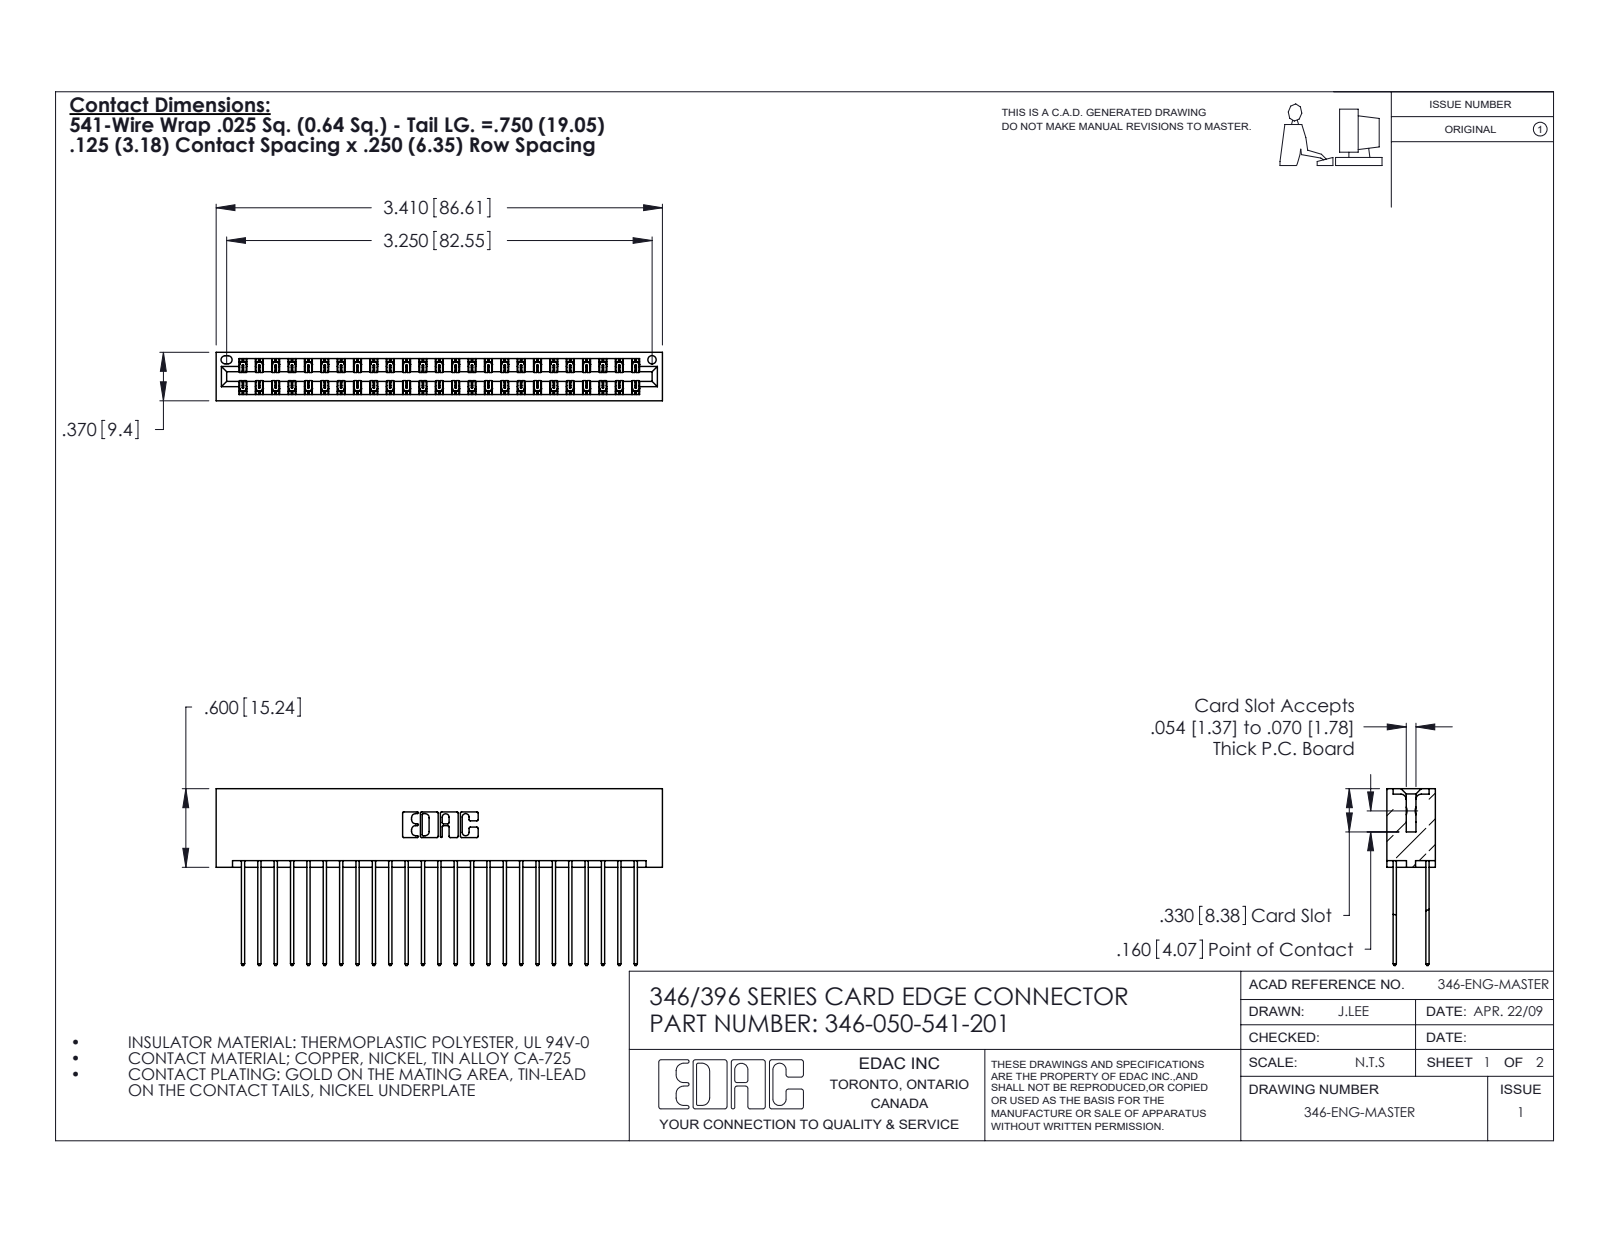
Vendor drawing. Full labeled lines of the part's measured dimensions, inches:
Part name (STEP PRODUCT): 345-292-001_345-293-141; 346 Part_No Mounting Lugs; 346-050-541-201
STEP written by: SolidWorks 2020 (CONFIG_CONTROL_DESIGN)
Units: inches
Bodies: 51 solids, 2714 faces (1822 planar, 892 cylindrical, 0 other)
Overall size (bounding box): 3.41 × 1.35 × 0.37
Volume: 0.56 in³ · Surface area: 21.52 in²
Round holes (diameter × count): ⌀0.064 ×1
Partial cylindrical surfaces — rounded edges, fillets, slot ends (radius × count): R0.006 ×75, R0.01 ×50, R0.01 ×22, R0.007 ×6, R0.031 ×6, R0.026 ×3, R0.014 ×2, R0.022 ×2
Main face-to-face distances: 0.048, 0.322, 0.25, 0.072, 0.298, 0.025, 0.37, 0.275, 0.225, 0.148
